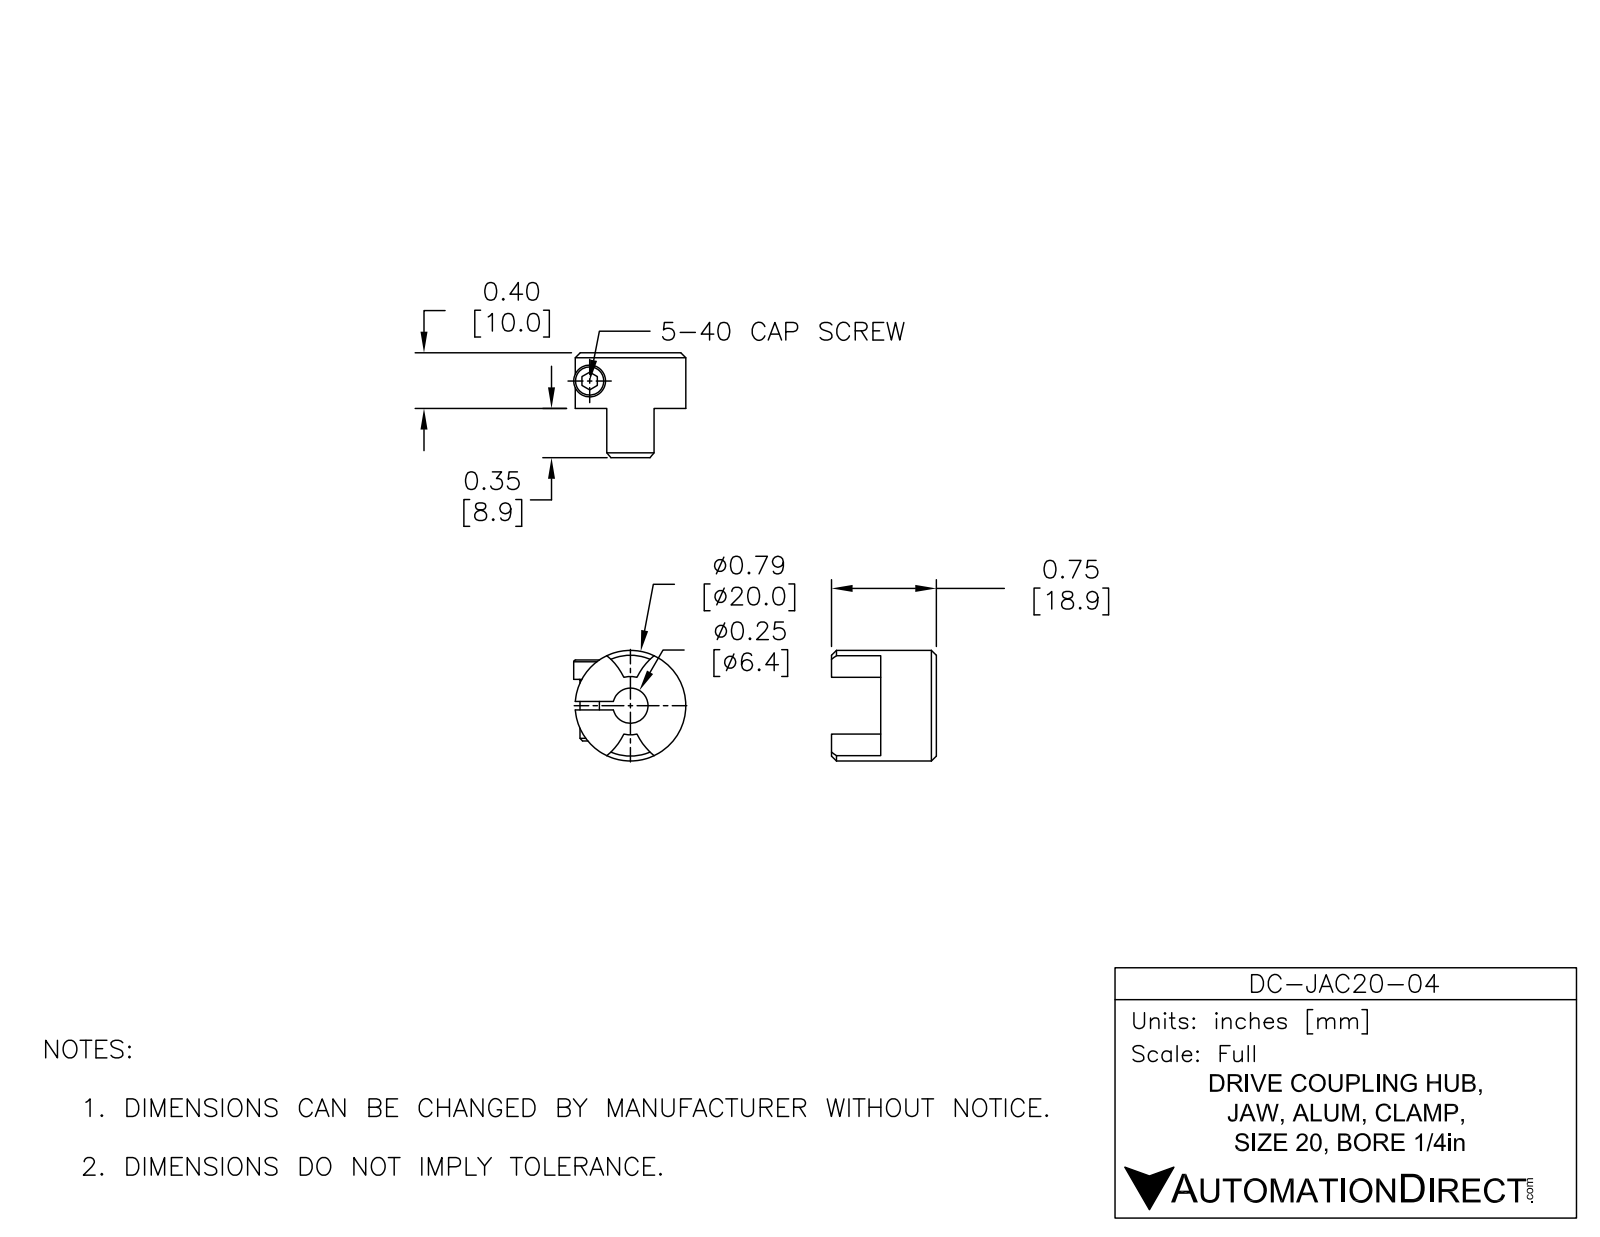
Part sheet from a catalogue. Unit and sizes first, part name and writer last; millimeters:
Units: millimetres
Overall size (bounding box): 19.96 × 19.93 × 18.92
Round holes (diameter × count): ⌀3.58 ×1, ⌀6.35 ×1
Round bosses / shafts (diameter × count): ⌀19.96 ×1
Partial cylindrical surfaces — rounded edges, fillets, slot ends (radius × count): R11.68 ×2, R2.78 ×1, R5.26 ×1
Main face-to-face distances: 10.03, 1.52, 18.92, 8.89, 3.99, 5.51
Volume: 2 985 mm³ · Surface area: 1 896 mm²
Bodies: 1 solid, 23 faces (7 planar, 13 cylindrical, 3 other)
Part name (STEP PRODUCT): DC-JAC20-04
STEP written by: SolidWorks 2015 (AUTOMOTIVE_DESIGN)
